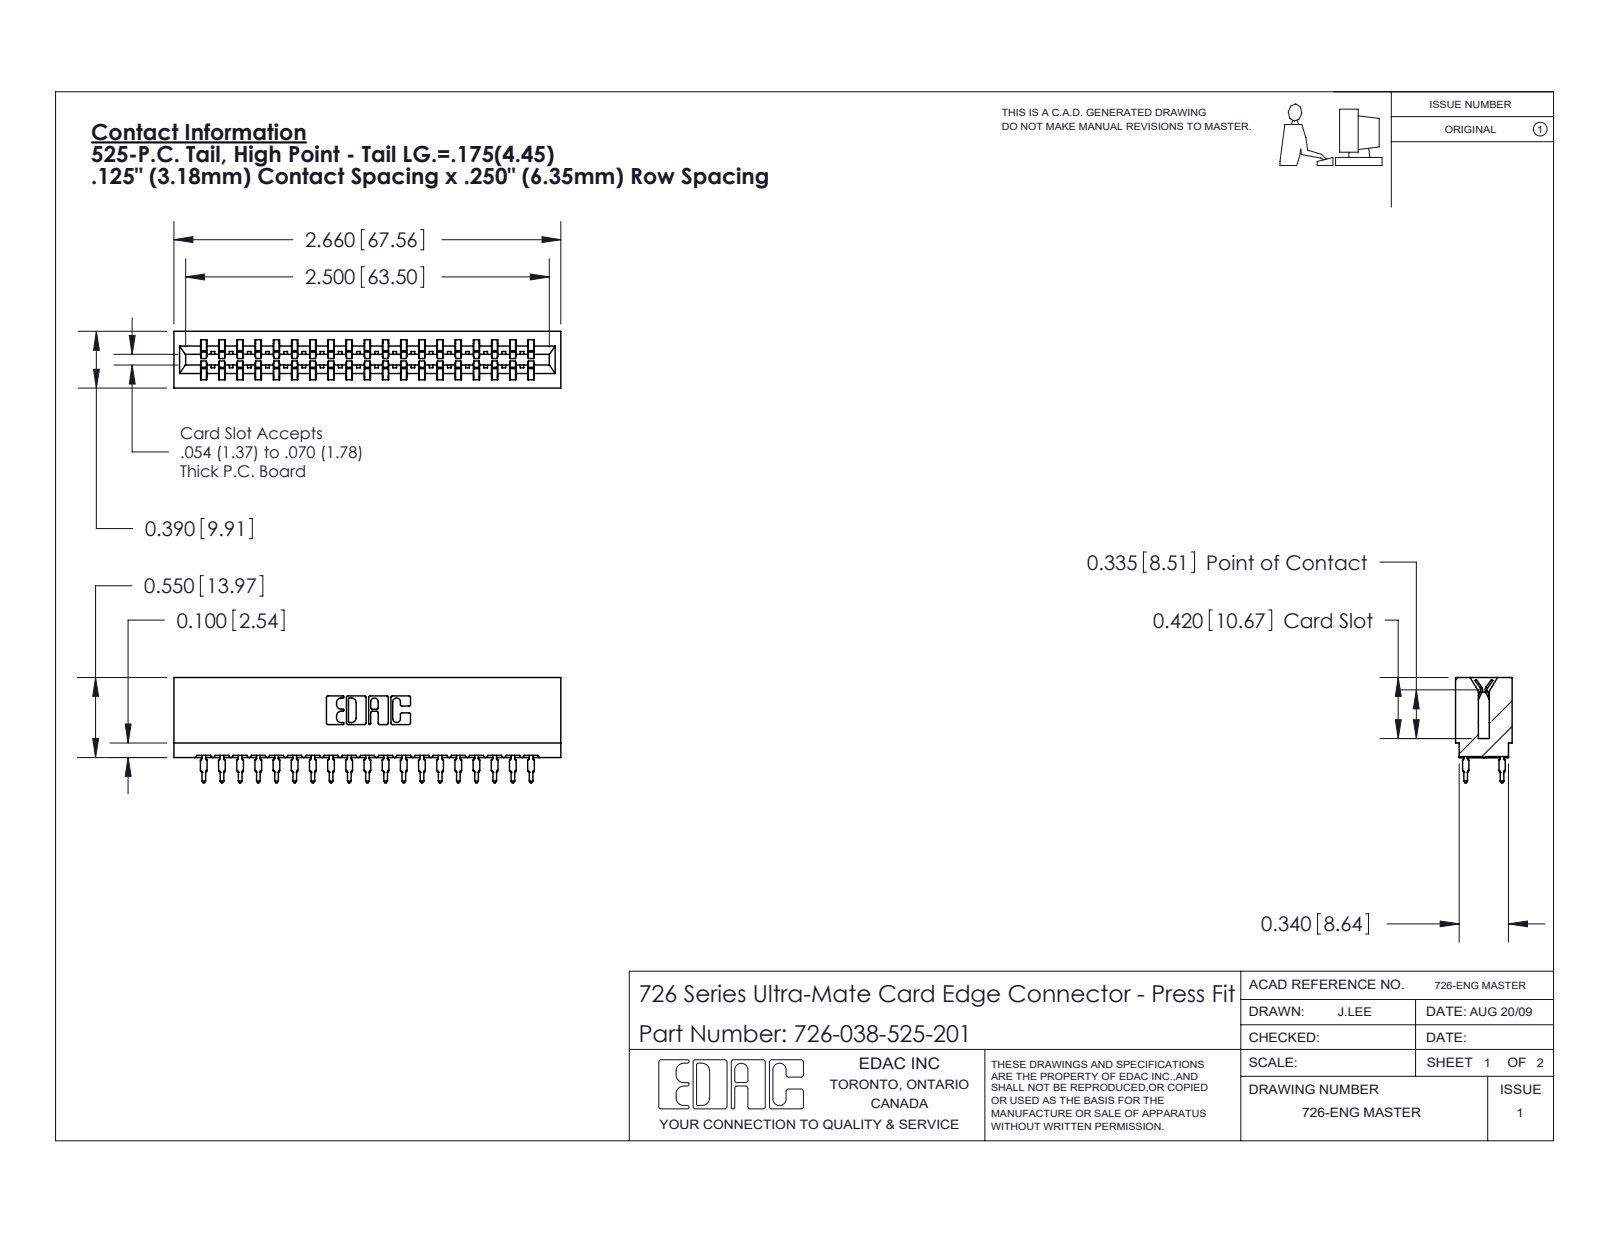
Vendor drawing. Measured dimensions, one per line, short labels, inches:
name: 726-038-525-201; 726 Part_.515 Slot Depth - 01; 746-292-001_525
written by: SolidWorks 2020 (CONFIG_CONTROL_DESIGN)
unit: in
bodies: 39 solids, 3498 faces (1803 planar, 707 cylindrical, 988 other)
size: 2.66 × 0.724 × 0.39
volume: 0.386 in³; area: 15.56 in²
rounds: 76× R0.021, 22× R0.01, 20× R0.015, 8× R0.005, 8× R0.011, 6× R0.007, 6× R0.031, 3× R0.026
face distances: 0.057, 0.333, 0.25, 0.39, 0.5, 0.025, 0.307, 0.125, 0.75, 0.275
